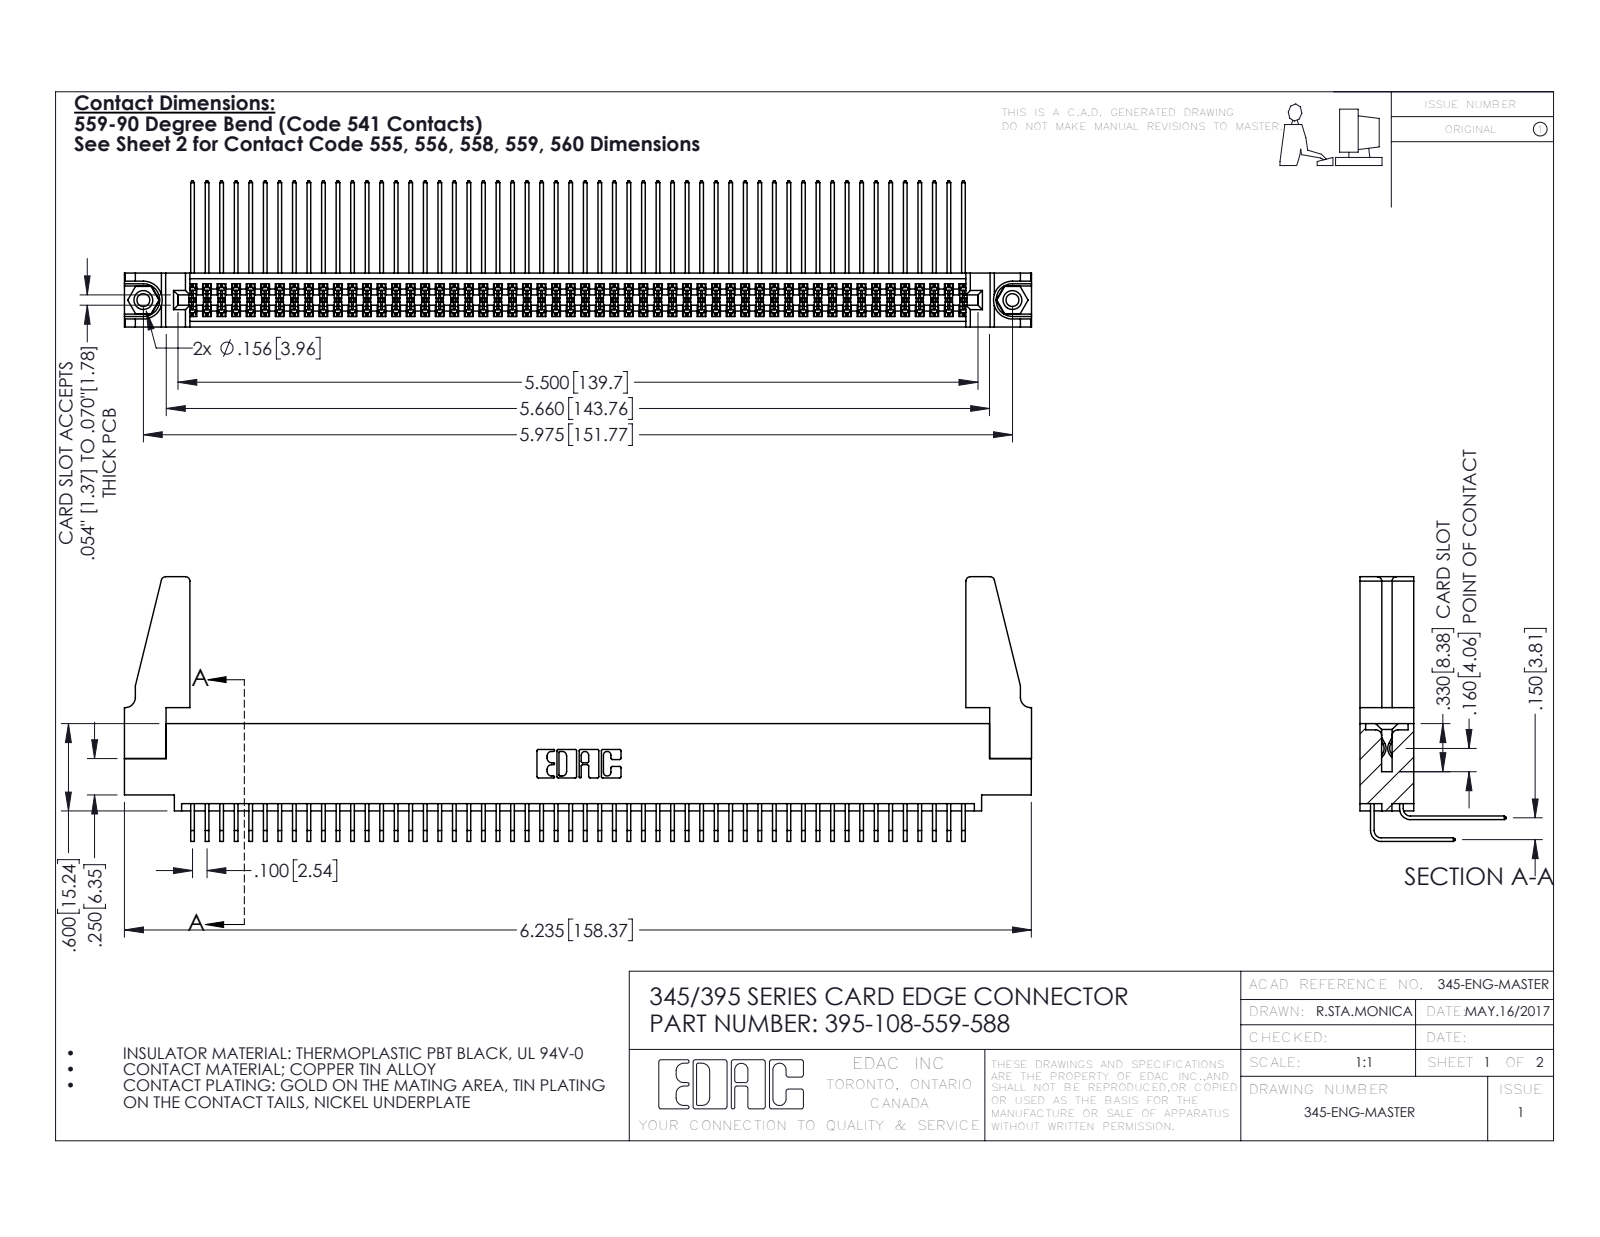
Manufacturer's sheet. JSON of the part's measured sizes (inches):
{"part_name": "345-292-001_558 559 Tail - 1; 395-108-559-588; 345-220-078_345-220-088; 345-292-001_559 Tail - 2 (+2 more)", "step_written_by": "SolidWorks 2016 (CONFIG_CONTROL_DESIGN)", "units": "inches", "bodies": {"solids": 113, "faces": 5870, "planar": 3936, "cylindrical": 1918, "other": 16}, "overall_size": [6.236, 1.819, 1.005], "volume_in3": 1.178, "surface_area_in2": 46.65, "round_holes": [[0.089, 2], [0.125, 2], [0.156, 2], [0.064, 1]], "round_bosses_or_shafts": [[0.155, 2]], "partial_cylinders_radius": [[0.006, 162], [0.01, 22], [0.03, 8], [0.007, 6], [0.031, 6], [0.026, 3], [0.014, 2], [0.019, 2]], "face_to_face_distances": [0.072, 0.298, 0.37, 0.2, 0.098, 0.272, 0.025, 0.225, 0.175, 0.15], "hole_center_spacings": [0.27, 5.739, 5.975]}
